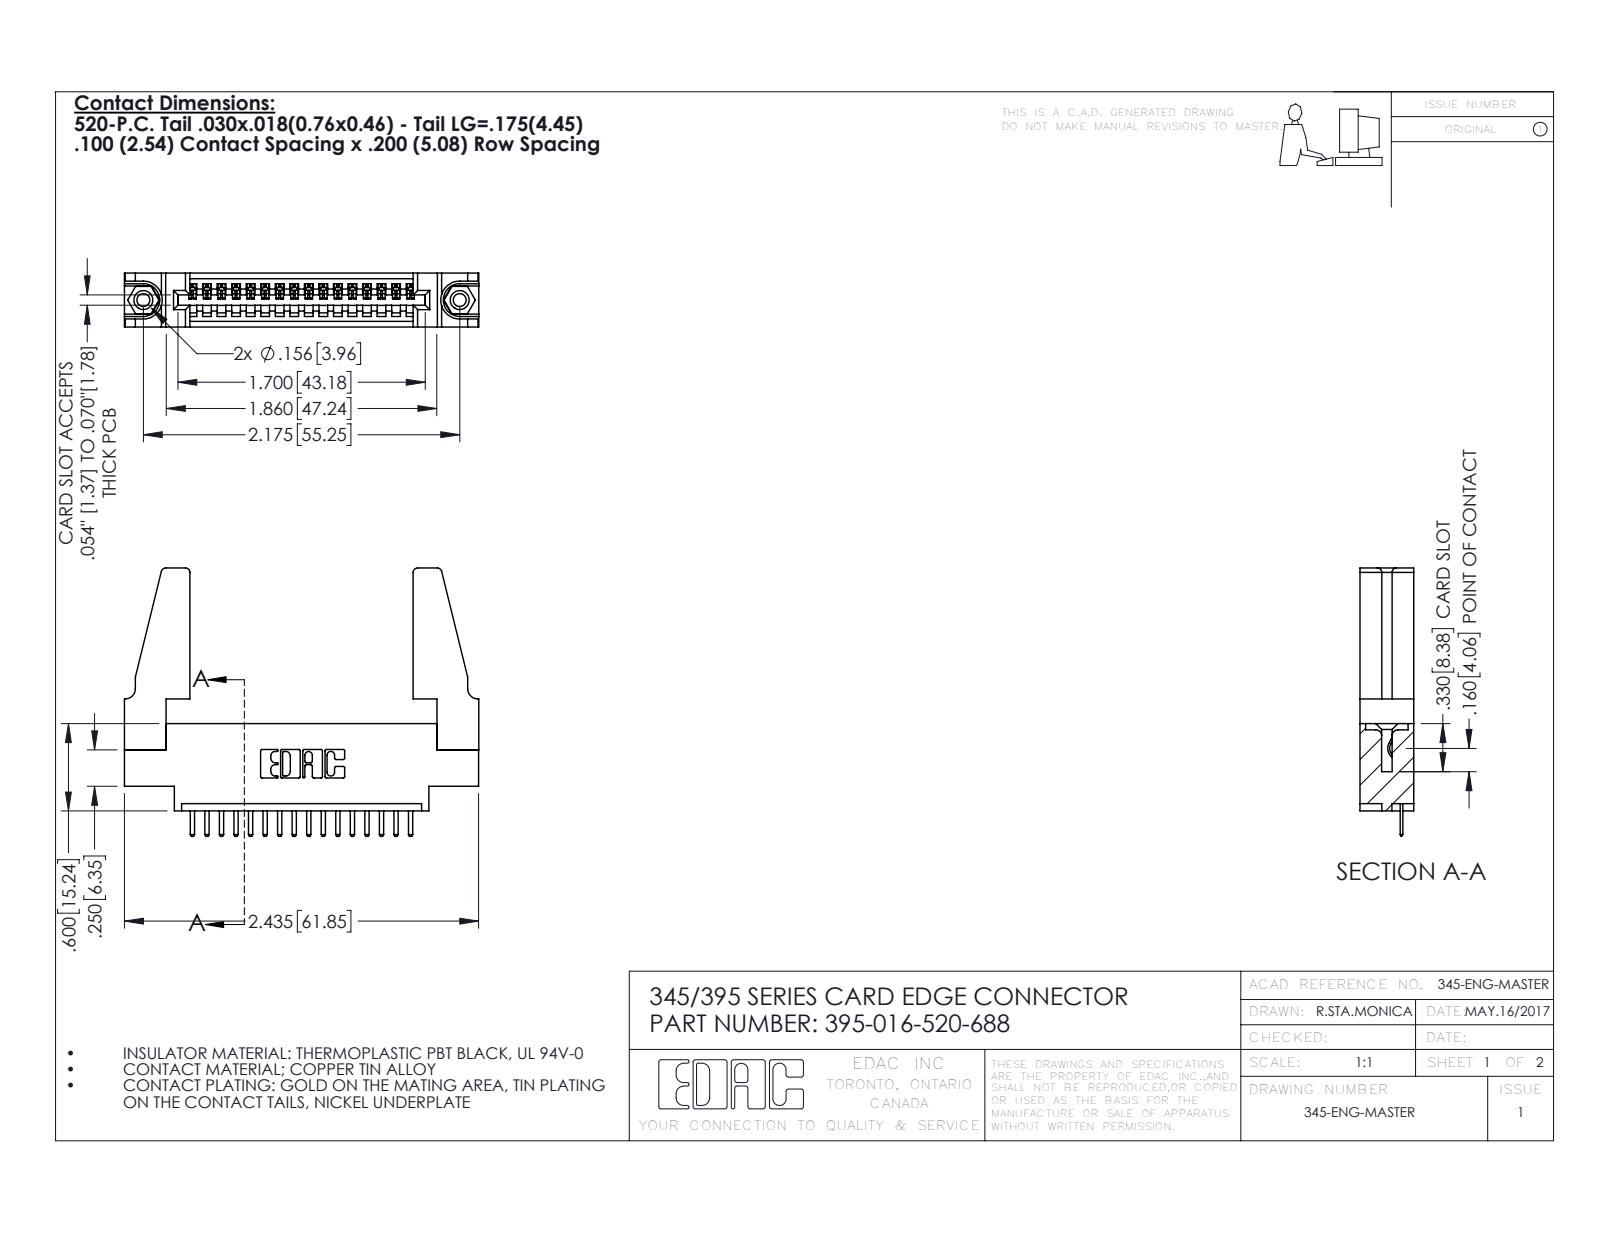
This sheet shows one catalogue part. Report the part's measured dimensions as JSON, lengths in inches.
{"part_name": "345 Part_0.170 Offset - 0.156 Dia-TH; 395-016-520-688; 345-220-078_345-220-088; 345-250-001_345-250-001-102 (+1 more)", "step_written_by": "SolidWorks 2016 (CONFIG_CONTROL_DESIGN)", "units": "inches", "bodies": {"solids": 21, "faces": 1246, "planar": 828, "cylindrical": 402, "other": 16}, "overall_size": [2.436, 1.845, 0.37], "volume_in3": 0.534, "surface_area_in2": 15.6, "round_holes": [[0.089, 2], [0.125, 2], [0.156, 2], [0.064, 1]], "round_bosses_or_shafts": [[0.155, 2]], "partial_cylinders_radius": [[0.01, 34], [0.006, 32], [0.01, 22], [0.03, 8], [0.007, 6], [0.031, 6], [0.026, 3], [0.031, 2]], "face_to_face_distances": [0.37, 0.072, 0.298, 0.2, 0.098, 0.272, 0.025, 0.225, 0.148, 0.15], "hole_center_spacings": [0.27, 1.942, 2.175]}
